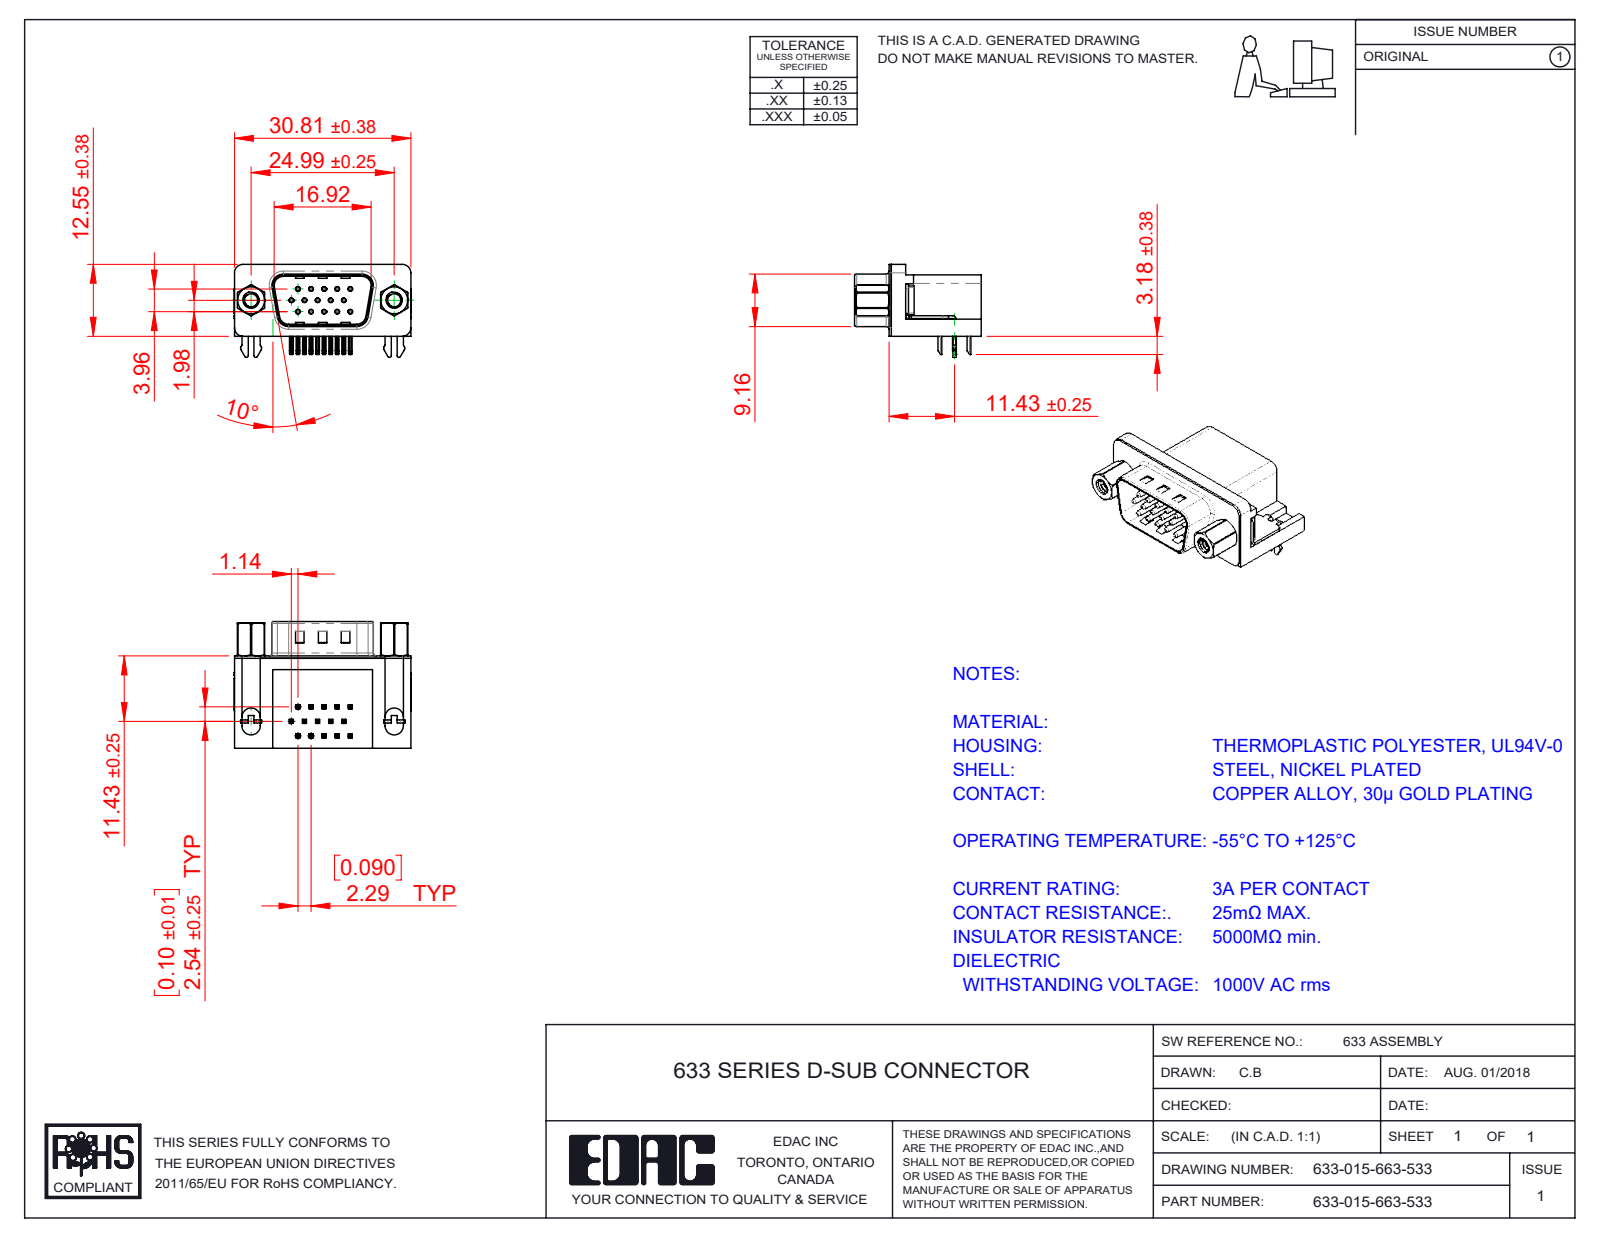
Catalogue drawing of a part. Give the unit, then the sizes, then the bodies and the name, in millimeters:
Units: millimetres
Overall size (bounding box): 30.89 × 22.1 × 16.25
Round holes (diameter × count): ⌀0.35 ×15, ⌀0.8 ×15, ⌀2.26 ×2, ⌀2.29 ×2, ⌀4 ×2, ⌀4.8 ×2, ⌀5 ×2
Round bosses / shafts (diameter × count): ⌀0.75 ×15, ⌀4.9 ×2, ⌀4.75 ×2, ⌀3.9 ×2, ⌀2.79 ×2
Partial cylindrical surfaces — rounded edges, fillets, slot ends (radius × count): R0.25 ×68, R0.12 ×30, R1 ×16, R0.5 ×14, R1.6 ×8, R1.5 ×7, R0.32 ×4, R0.9 ×4
Main face-to-face distances: 0.4, 10.35, 15.7, 16.1, 2.9, 0.5, 2.5, 6.7, 0.35, 10.7
Hole centre spacings: 3.96, 2.28, 4.57, 2.29, 6.05, 6.86, 7.92, 6.04
Volume: 4 275 mm³ · Surface area: 5 883 mm²
Bodies: 23 solids, 1603 faces (915 planar, 515 cylindrical, 173 other)
Part name (STEP PRODUCT): 633 4-40 Threaded Rivet; 633 Contact Middle; 633 Contact Bottom; 633 Shell_15 Contact (+5 more)
STEP written by: SolidWorks 2016 (CONFIG_CONTROL_DESIGN)
